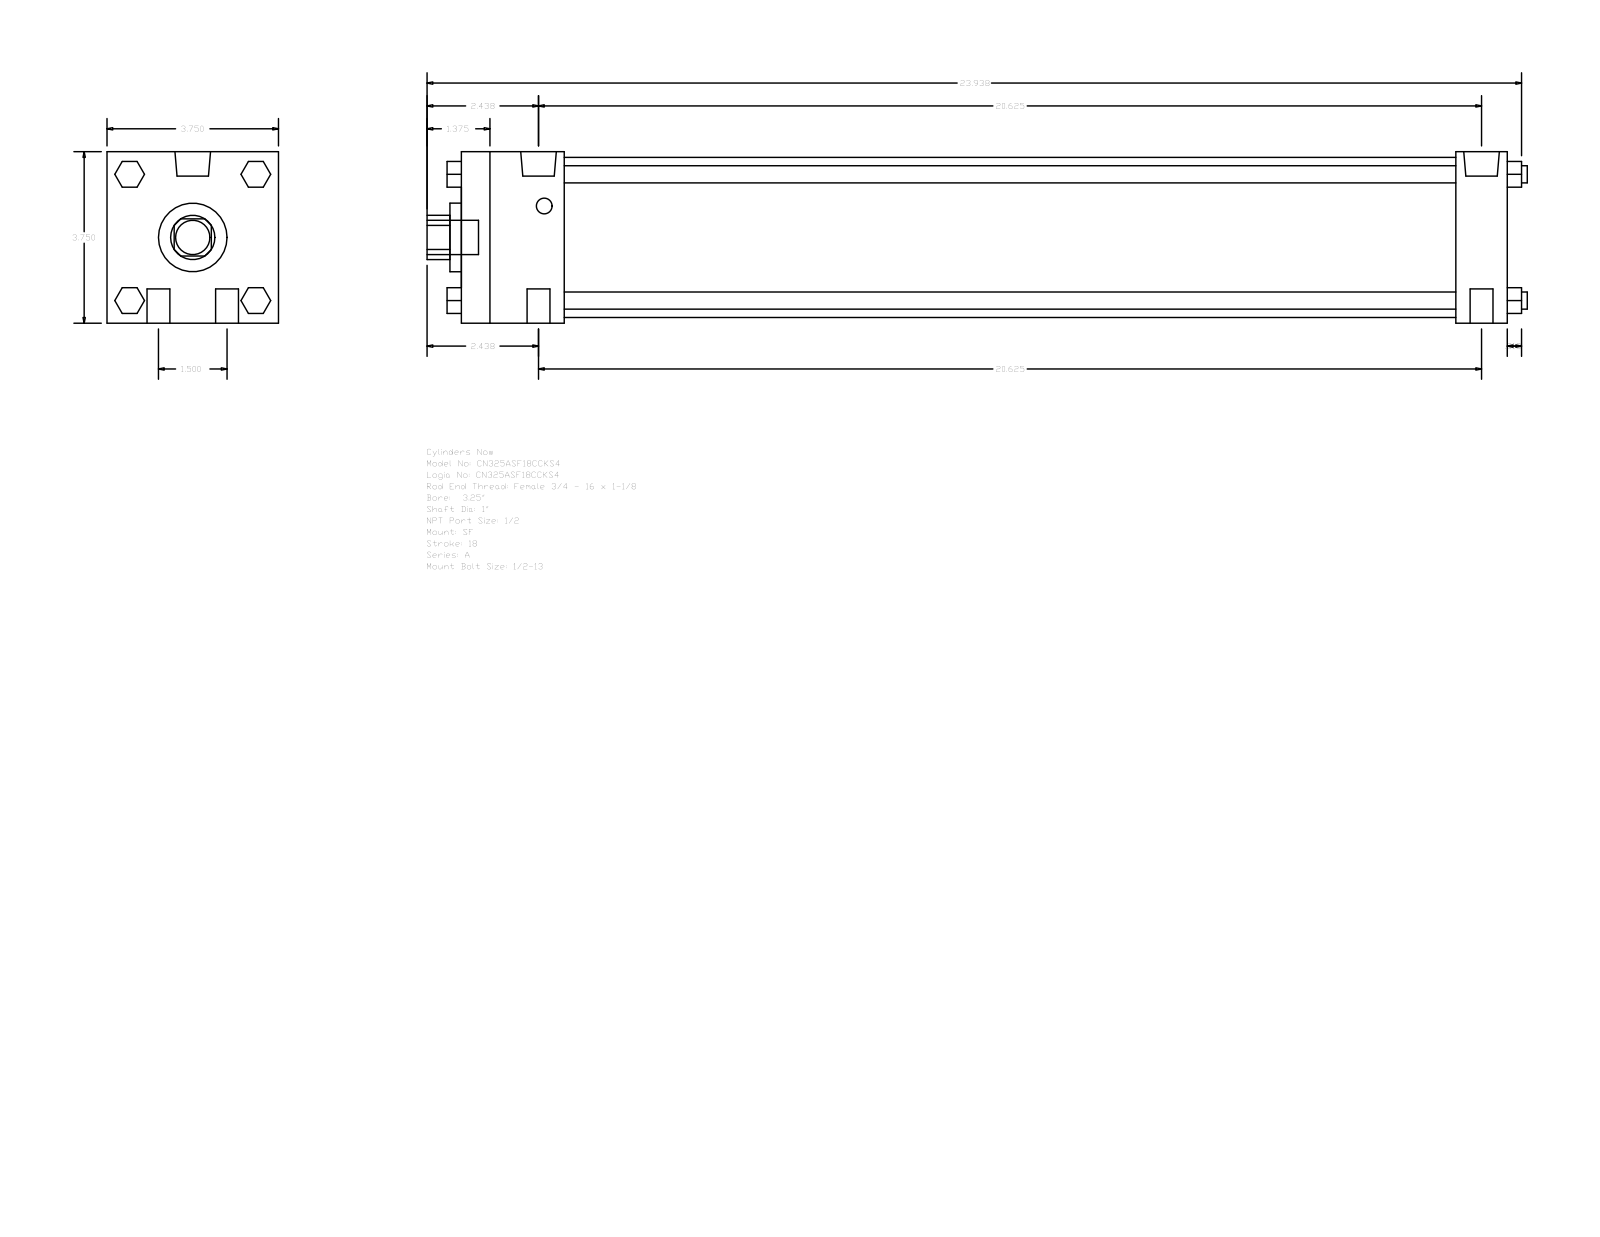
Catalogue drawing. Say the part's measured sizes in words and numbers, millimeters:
The part is named "A_SF__0325_1". Its 3-D file was written by "GSSL Pune (CONFIG_CONTROL_DESIGN)". It is 0 solids with 124 faces: 94 planar, 30 cylindrical and 0 other. Overall it measures 611.19 by 95.25 by 95.25 millimeters. Round holes: 1 of diameter 25.4, 1 of diameter 38.1, 1 of diameter 88.9. Round bosses or shafts: 4 of diameter 12.7, 4 of diameter 9.53, 2 of diameter 19.77, 2 of diameter 8.73, 1 of diameter 19.05. Partial cylindrical surfaces (rounded edges, fillets, slot ends): 1 of radius 12.29. The main face-to-face distances are 95.24, 581.03, 552.45, 28.58, 57.15, 495.3, 523.88, 14.28, 35.05, 60.71.
